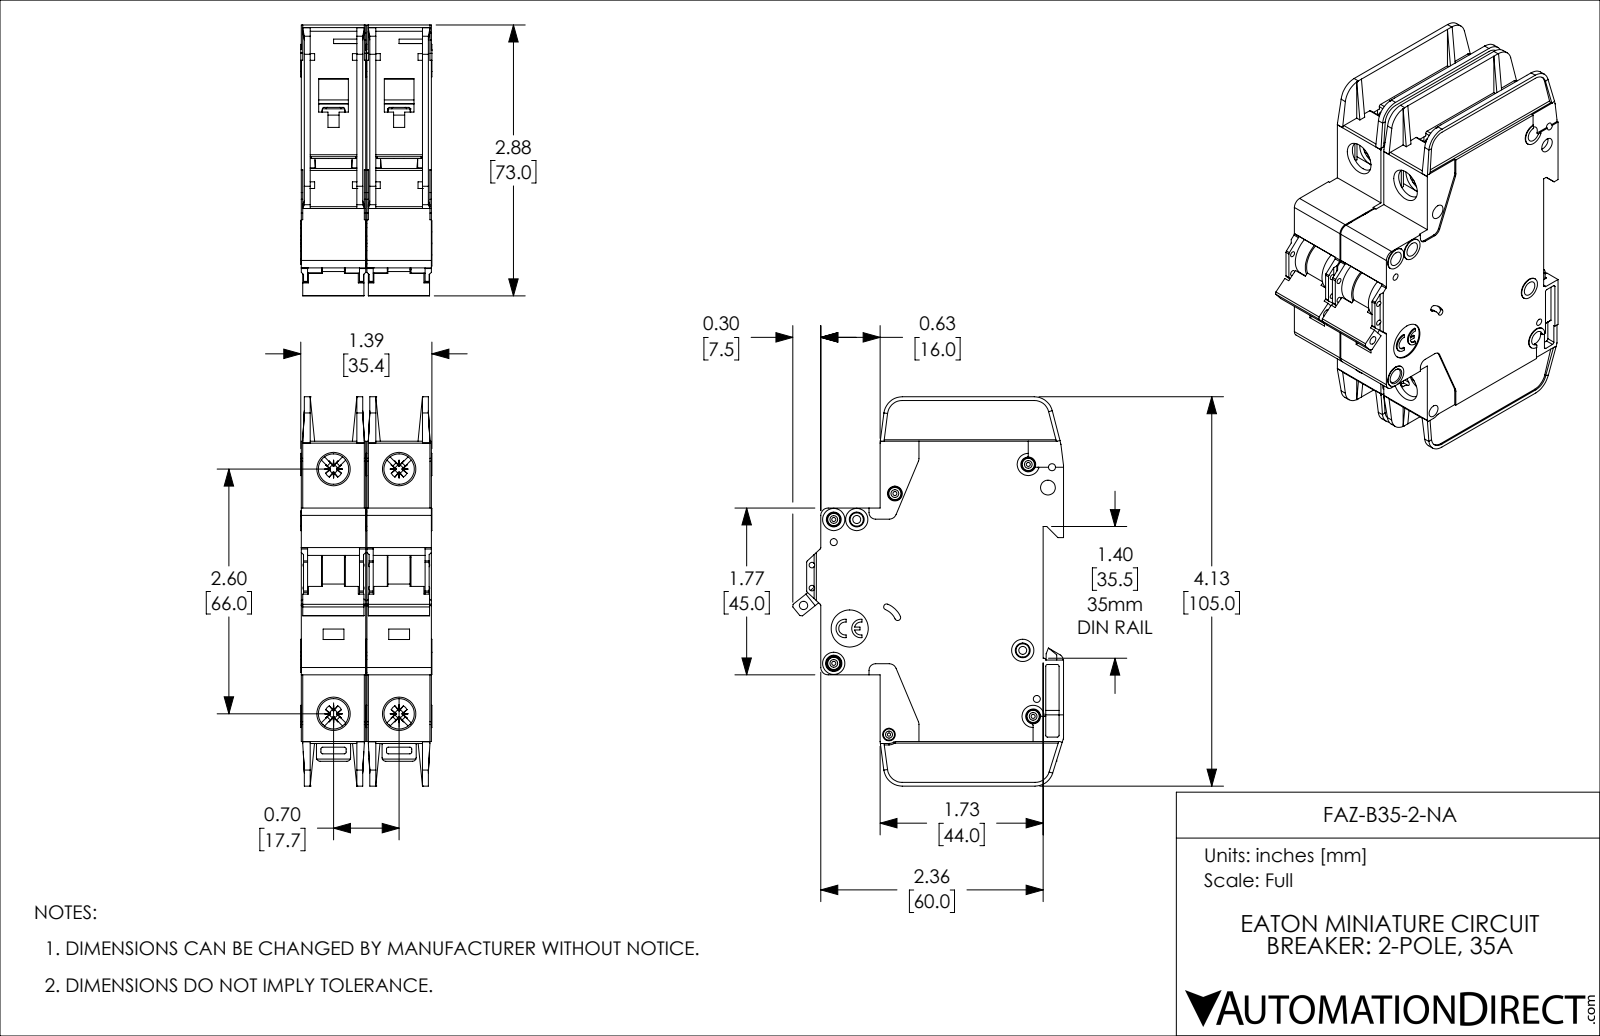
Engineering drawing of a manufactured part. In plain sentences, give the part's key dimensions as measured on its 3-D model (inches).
The part is named "FAZ-B35-2-NA". Its 3-D file was written by "SolidWorks 2019 (AUTOMOTIVE_DESIGN)". It is 2 solids with 2254 faces: 1342 planar, 714 cylindrical and 198 other. Overall it measures 4.134 by 2.876 by 1.394 inches. Its volume is 9.365 cubic inches and its surface area 82.01 square inches. Round holes: 8 of diameter 0.157, 5 of diameter 0.043, 4 of diameter 0.075, 4 of diameter 0.323, 2 of diameter 0.059, 2 of diameter 0.085, 1 of diameter 0.035, 1 of diameter 0.089, 1 of diameter 0.098, 1 of diameter 0.134, 1 of diameter 0.394. Round bosses or shafts: 5 of diameter 0.13, 4 of diameter 0.236, 3 of diameter 0.118, 2 of diameter 0.098. Partial cylindrical surfaces (rounded edges, fillets, slot ends): 57 of radius 0.02, 20 of radius 0.016, 14 of radius 0.039, 10 of radius 0.079, 8 of radius 0.043, 5 of radius 0.008, 5 of radius 0.197, 4 of radius 0.01. The main face-to-face distances are 0.697, 0.047, 0.685, 0.591, 0.094, 0.638, 0.543, 1.382, 0.744, 0.65. The hole center spacings are 0.244, 0.537, 0.697, 0.87, 2.598, 2.69, 0.189, 0.199.
